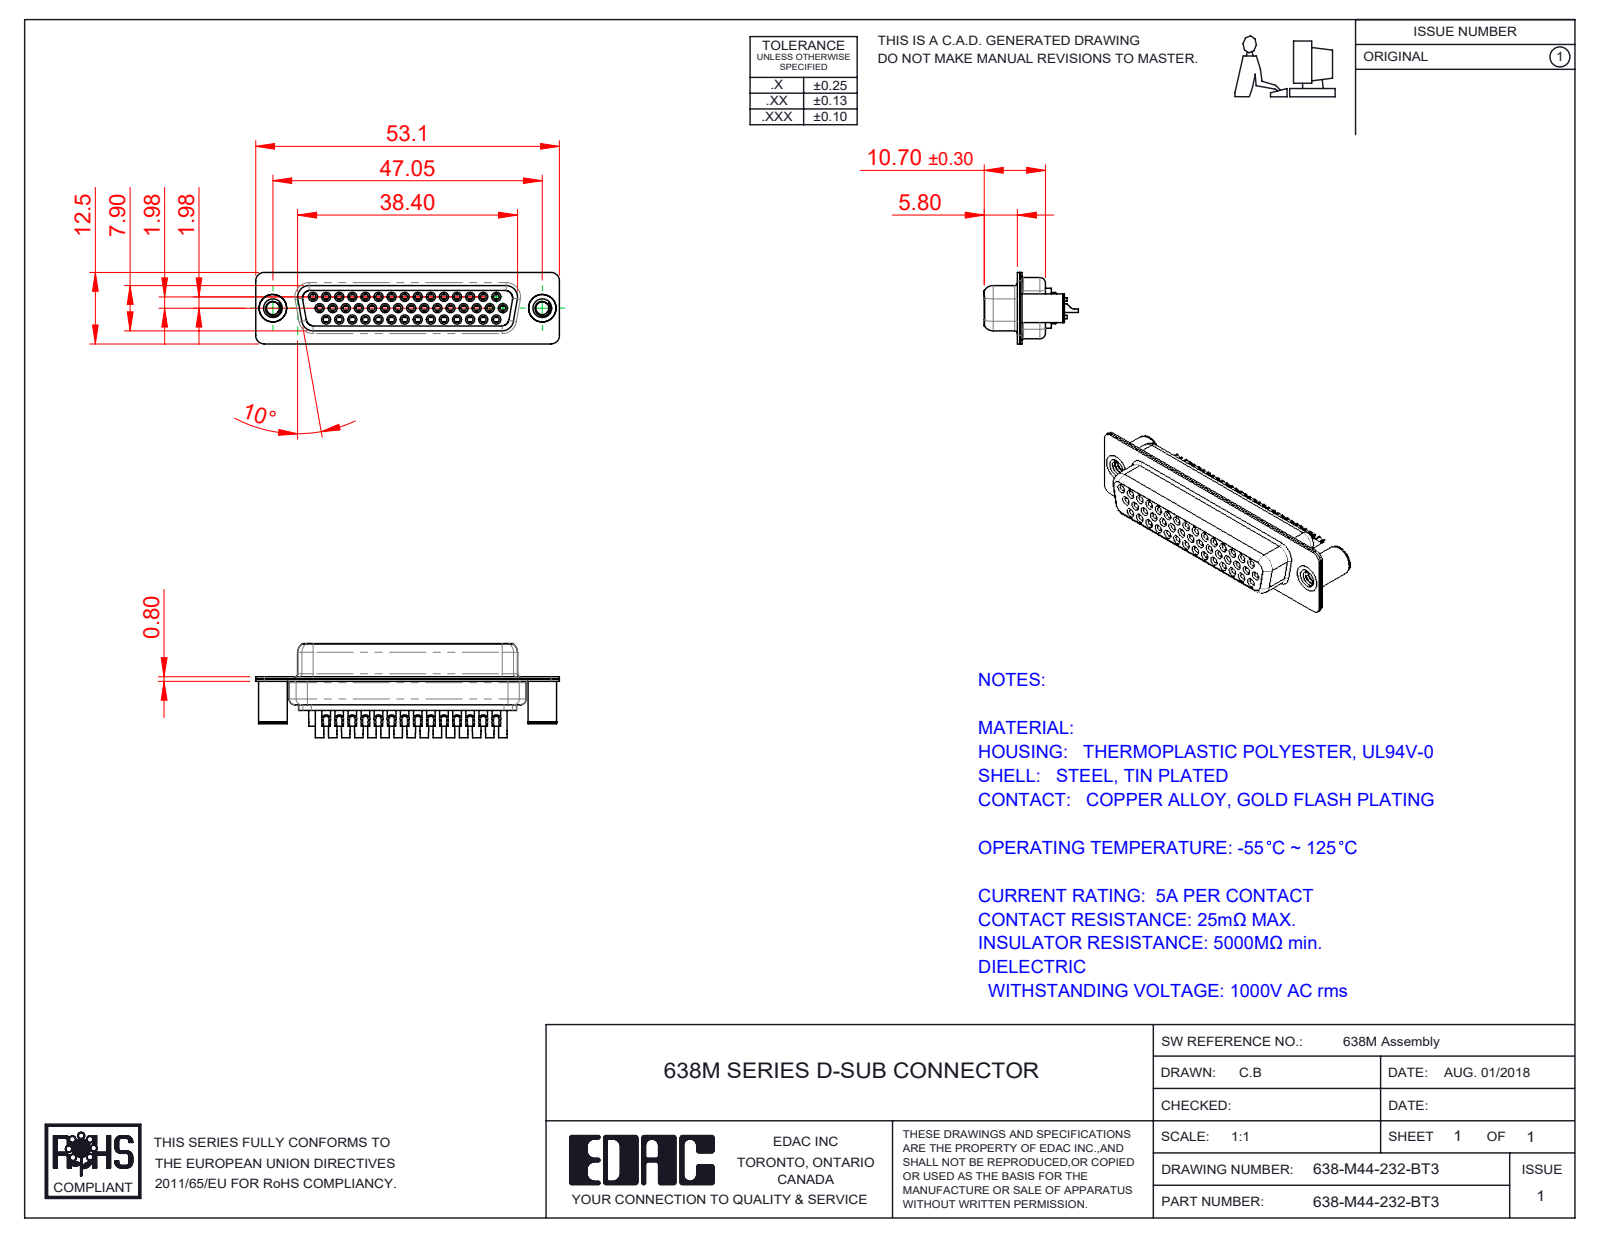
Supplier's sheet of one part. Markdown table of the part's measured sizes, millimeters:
| quantity | value |
| --- | --- |
| part name | 638-M44-232-BT3; 638M Housing_44 Contacts; 638M 4-40 Threaded Board Spacer; 638M Shell Front_44 Contacts (+4 more) |
| STEP written by | SolidWorks 2020 (CONFIG_CONTROL_DESIGN) |
| units | millimeters |
| bodies | 49 solids, 2733 faces (815 planar, 1085 cylindrical, 833 other) |
| overall size | 53.05 × 16.45 × 12.5 |
| volume | 3 724 mm³ |
| surface area | 12 586 mm² |
| round holes (diameter × count) | 1 × 44, 1.1 × 44, 1.7 × 44, 1.8 × 44, 2 × 44, 2.26 × 2, 3.26 × 2, 4 × 2, 4.8 × 2 |
| round bosses / shafts (diameter × count) | 2.2 × 44, 1.6 × 44, 1.5 × 44, 5 × 2, 4.9 × 2 |
| partial cylindrical surfaces (radius × count) | 1.5 × 16, 2 × 12, 1.35 × 9, 1.6 × 8, 1 × 7, 0.25 × 4, 0.5 × 4, 0.6 × 4 |
| main face-to-face distances | 0.4, 1.4, 0.45, 8.45, 8.9, 1.8, 1, 6.2, 7.05, 1.85 |
| hole center spacings | 2.28, 2.29, 3.96, 4.57, 8.24, 6.86, 11.43, 14.99 |
